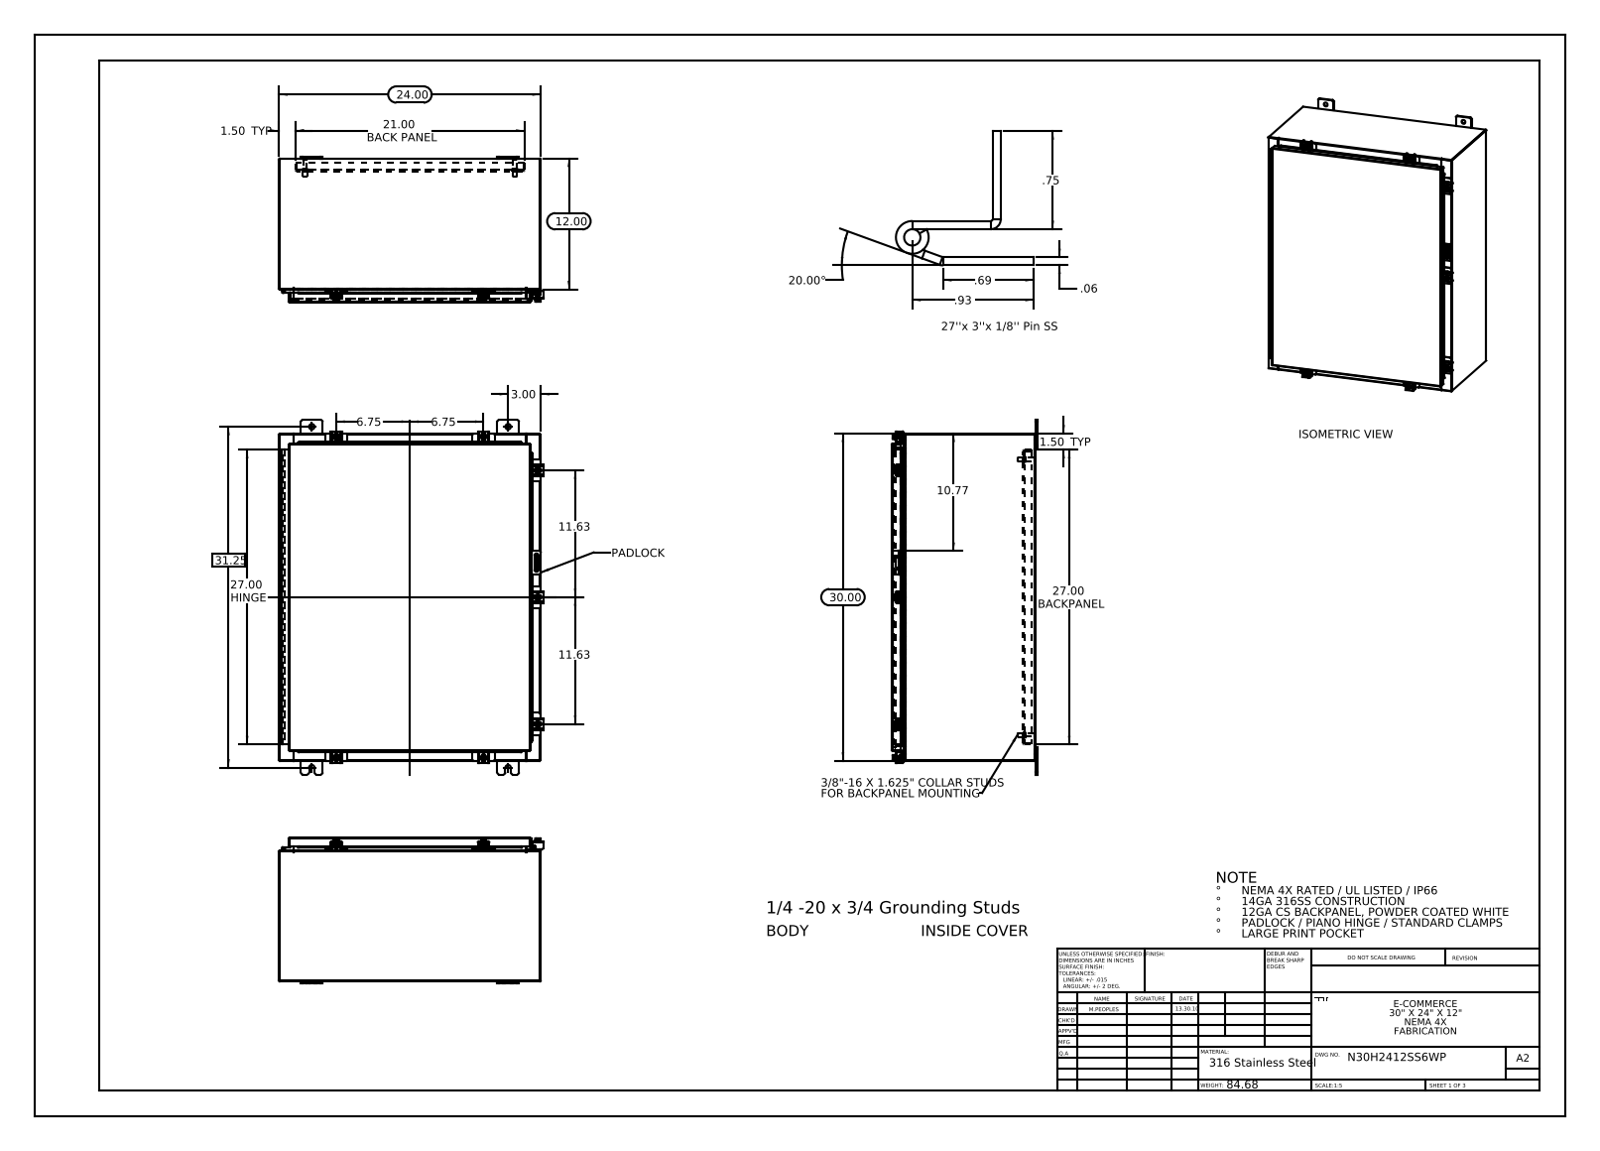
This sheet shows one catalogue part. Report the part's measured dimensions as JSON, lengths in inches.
{"part_name": "N30H2412SS6WP Clamp Assembly; N30H2412SS6WP Mounting Studs; N30H2412SS6WP Clamp Bracket; N30H2412SS6WP 22104005_DEFAULT (+8 more)", "step_written_by": "SolidWorks 2013 (CONFIG_CONTROL_DESIGN)", "units": "inches", "bodies": {"solids": 54, "faces": 2016, "planar": 1062, "cylindrical": 838, "other": 116}, "overall_size": [32.5, 24.211, 13.389], "volume_in3": 297, "surface_area_in2": 7481, "round_holes": [[0.5, 8], [0.213, 7], [0.26, 7], [0.125, 2], [0.125, 1]], "round_bosses_or_shafts": [[0.25, 8], [0.5, 7], [0.399, 7], [0.625, 4], [0.375, 4], [0.33, 4], [0.315, 2], [0.236, 2]], "partial_cylinders_radius": [[0.06, 34], [0.013, 27], [0.19, 24], [0.088, 21], [0.12, 14], [0.141, 14], [0.05, 11], [0.08, 10]], "face_to_face_distances": [0.075, 13.126, 23.925, 13.051, 13.201, 0.104, 1, 29.925, 1.075, 12.051], "hole_center_spacings": [27.501, 31.878, 1.858, 2.277, 2.326, 2.423, 3.561, 3.561]}
